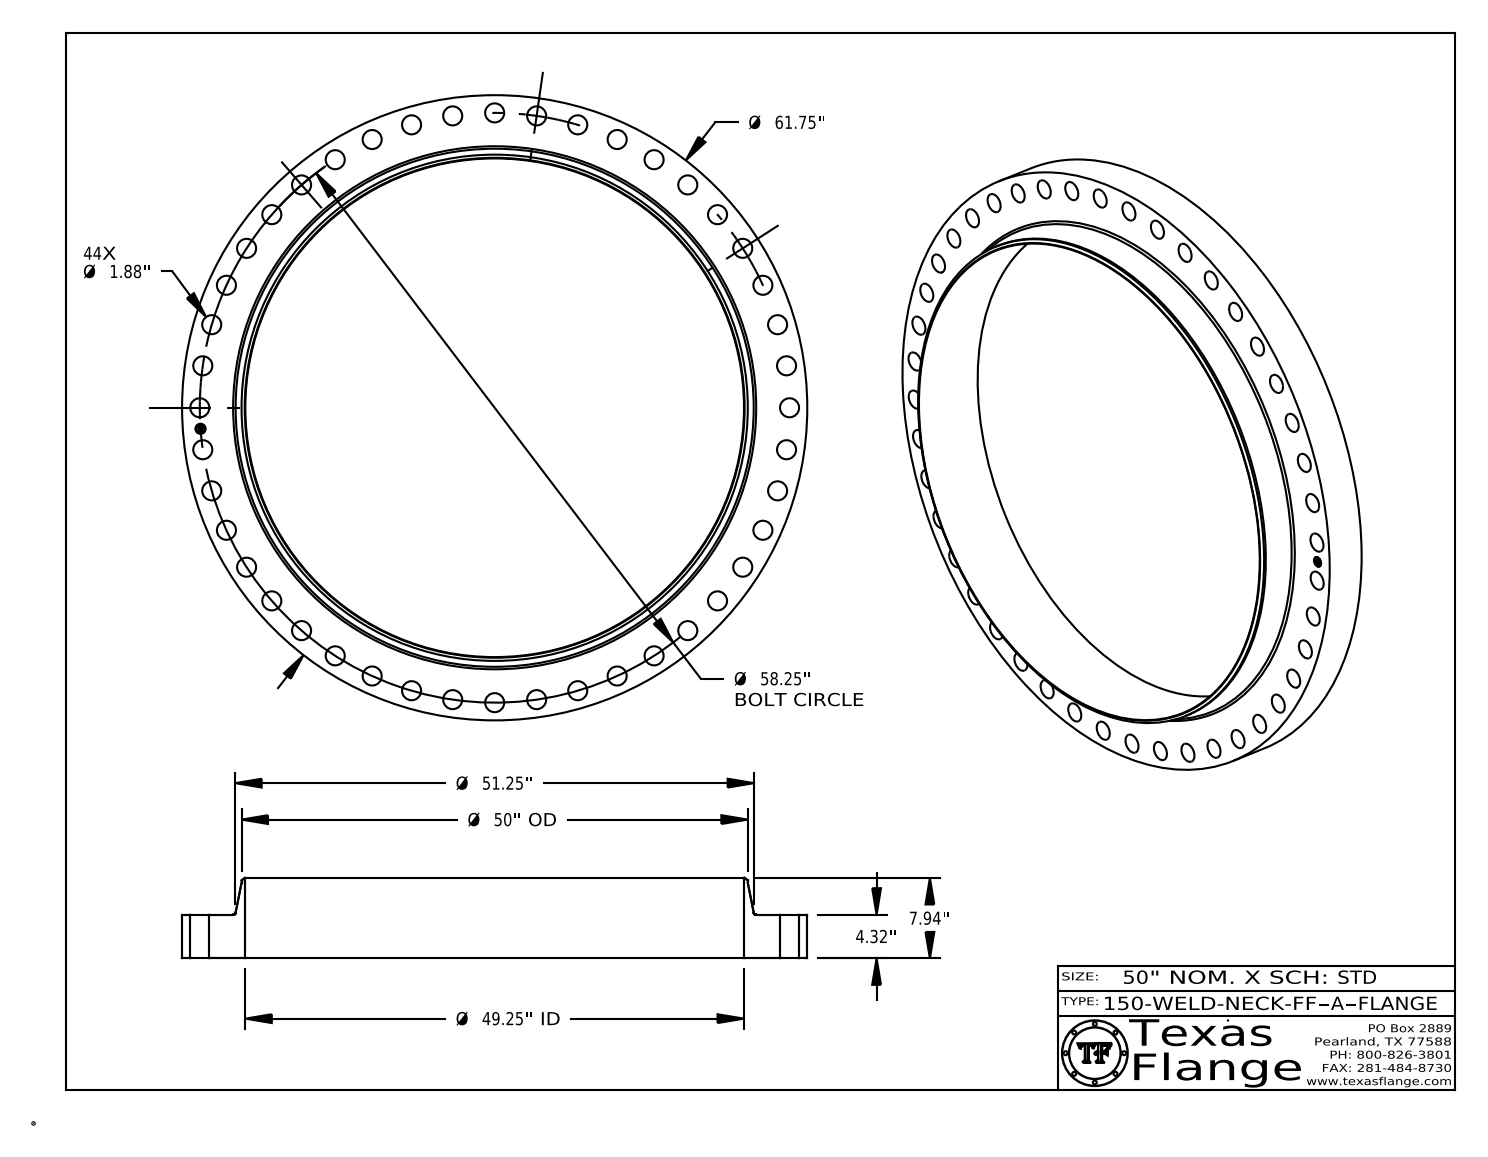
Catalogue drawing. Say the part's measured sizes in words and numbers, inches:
The part is named "150-WELD-NECK-FF, Series A". Its 3-D file was written by "CATIA V5 STEP AP214 (AUTOMOTIVE_DESIGN)". It is 1 solid with 488 faces: 368 planar, 114 cylindrical and 6 other. Overall it measures 61.75 by 61.75 by 7.94 inches. Its volume is 4 543 cubic inches and its surface area 5 574 square inches. Round holes: 44 of diameter 1.88, 1 of diameter 1, 1 of diameter 49.25. Round bosses or shafts: 8 of diameter 0.061, 1 of diameter 61.75, 1 of diameter 50, 1 of diameter 0.788. The main face-to-face distances are 4.32, 7.94, 3.62, 4.305, 0.015, 3.635, 0.298, 0.292, 0.054, 0.193. The hole center spacings are 8.29, 12.382, 4.156, 20.356, 29.125, 56.919, 55.891, 51.125.
